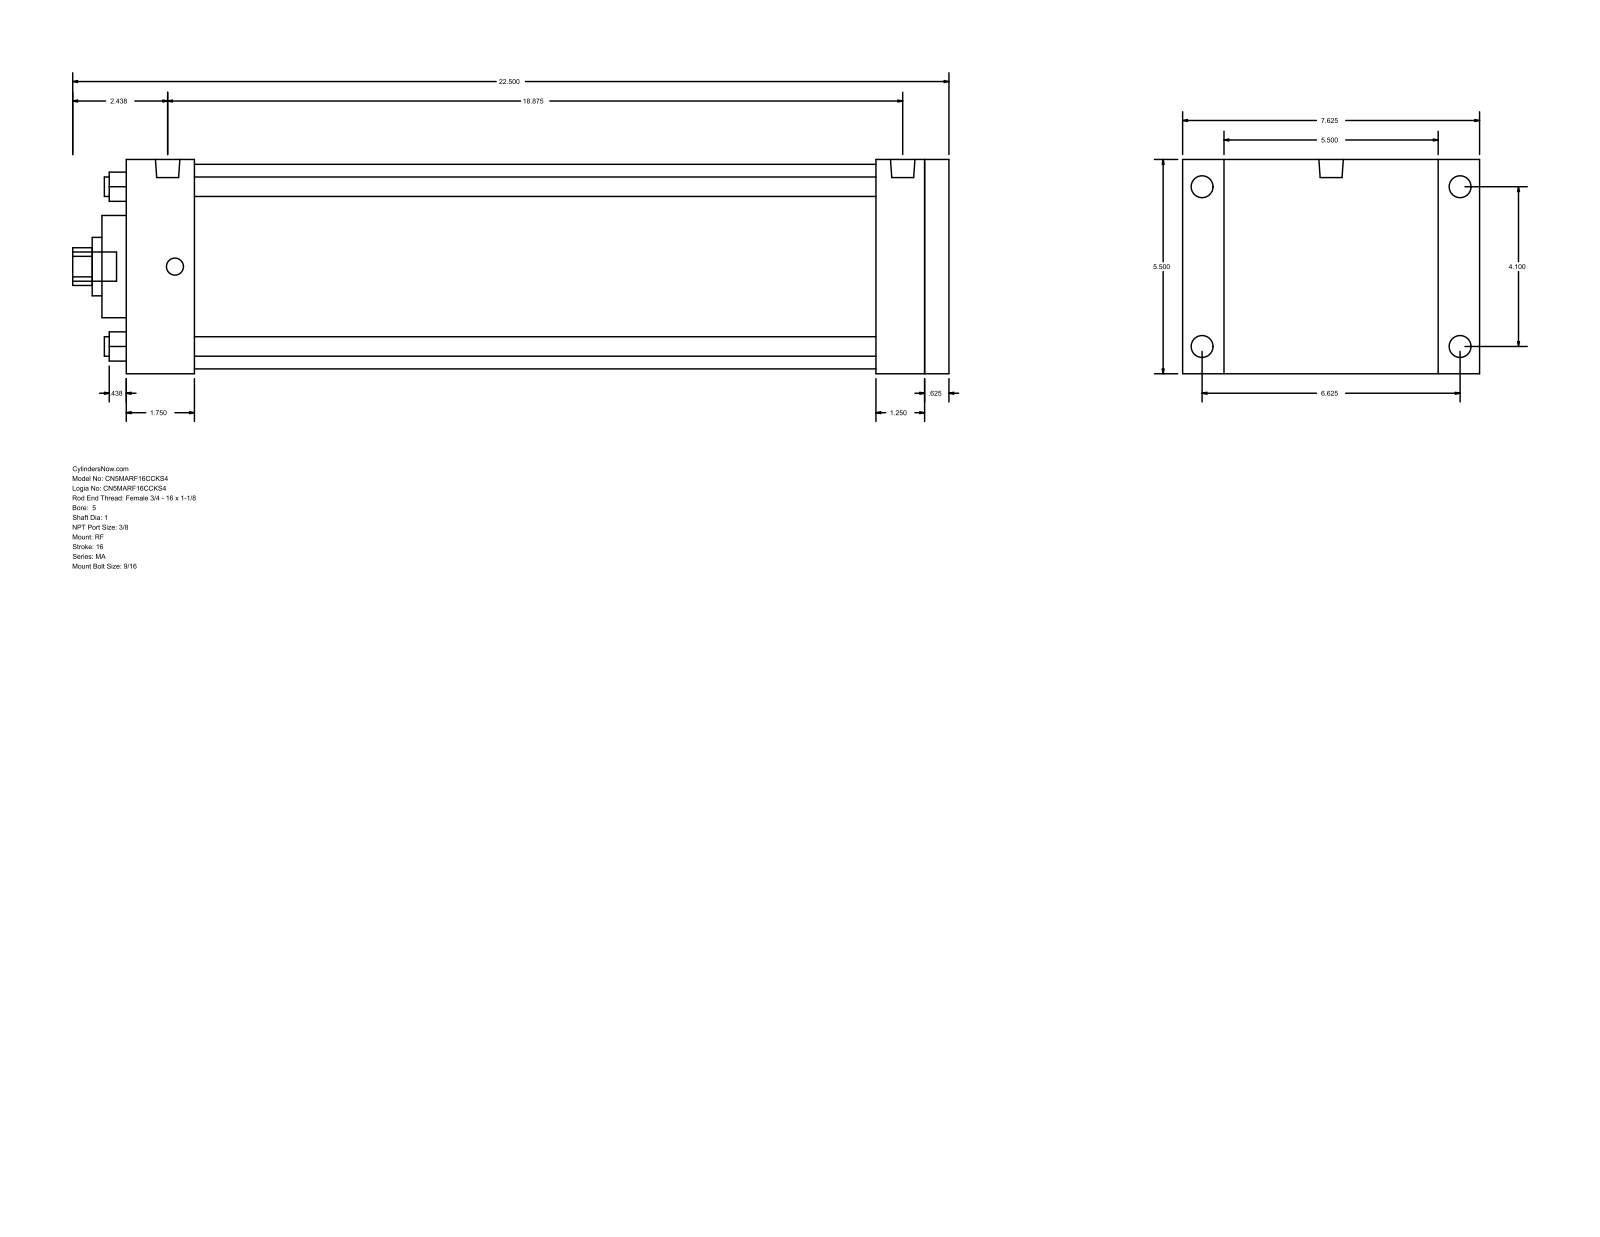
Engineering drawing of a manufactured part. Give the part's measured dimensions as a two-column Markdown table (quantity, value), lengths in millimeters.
| quantity | value |
| --- | --- |
| part name | MA_RF__0500_1 |
| STEP written by | GSSL Pune (CONFIG_CONTROL_DESIGN) |
| units | millimeters |
| bodies | 0 solids, 94 faces (65 planar, 29 cylindrical, 0 other) |
| overall size | 571.5 × 193.68 × 139.7 |
| round holes (diameter × count) | 12.7 × 4, 25.4 × 1, 38.1 × 1, 66.67 × 1, 133.35 × 1 |
| round bosses / shafts (diameter × count) | 14.29 × 4, 11.11 × 4, 15.93 × 2, 19.05 × 1 |
| partial cylindrical surfaces (radius × count) | 12.29 × 1 |
| main face-to-face distances | 139.7, 536.58, 520.7, 15.88, 44.46, 476.24, 492.12, 488.96, 444.5, 31.74 |
| hole center spacings | 73.64, 104.14, 147.28 |
